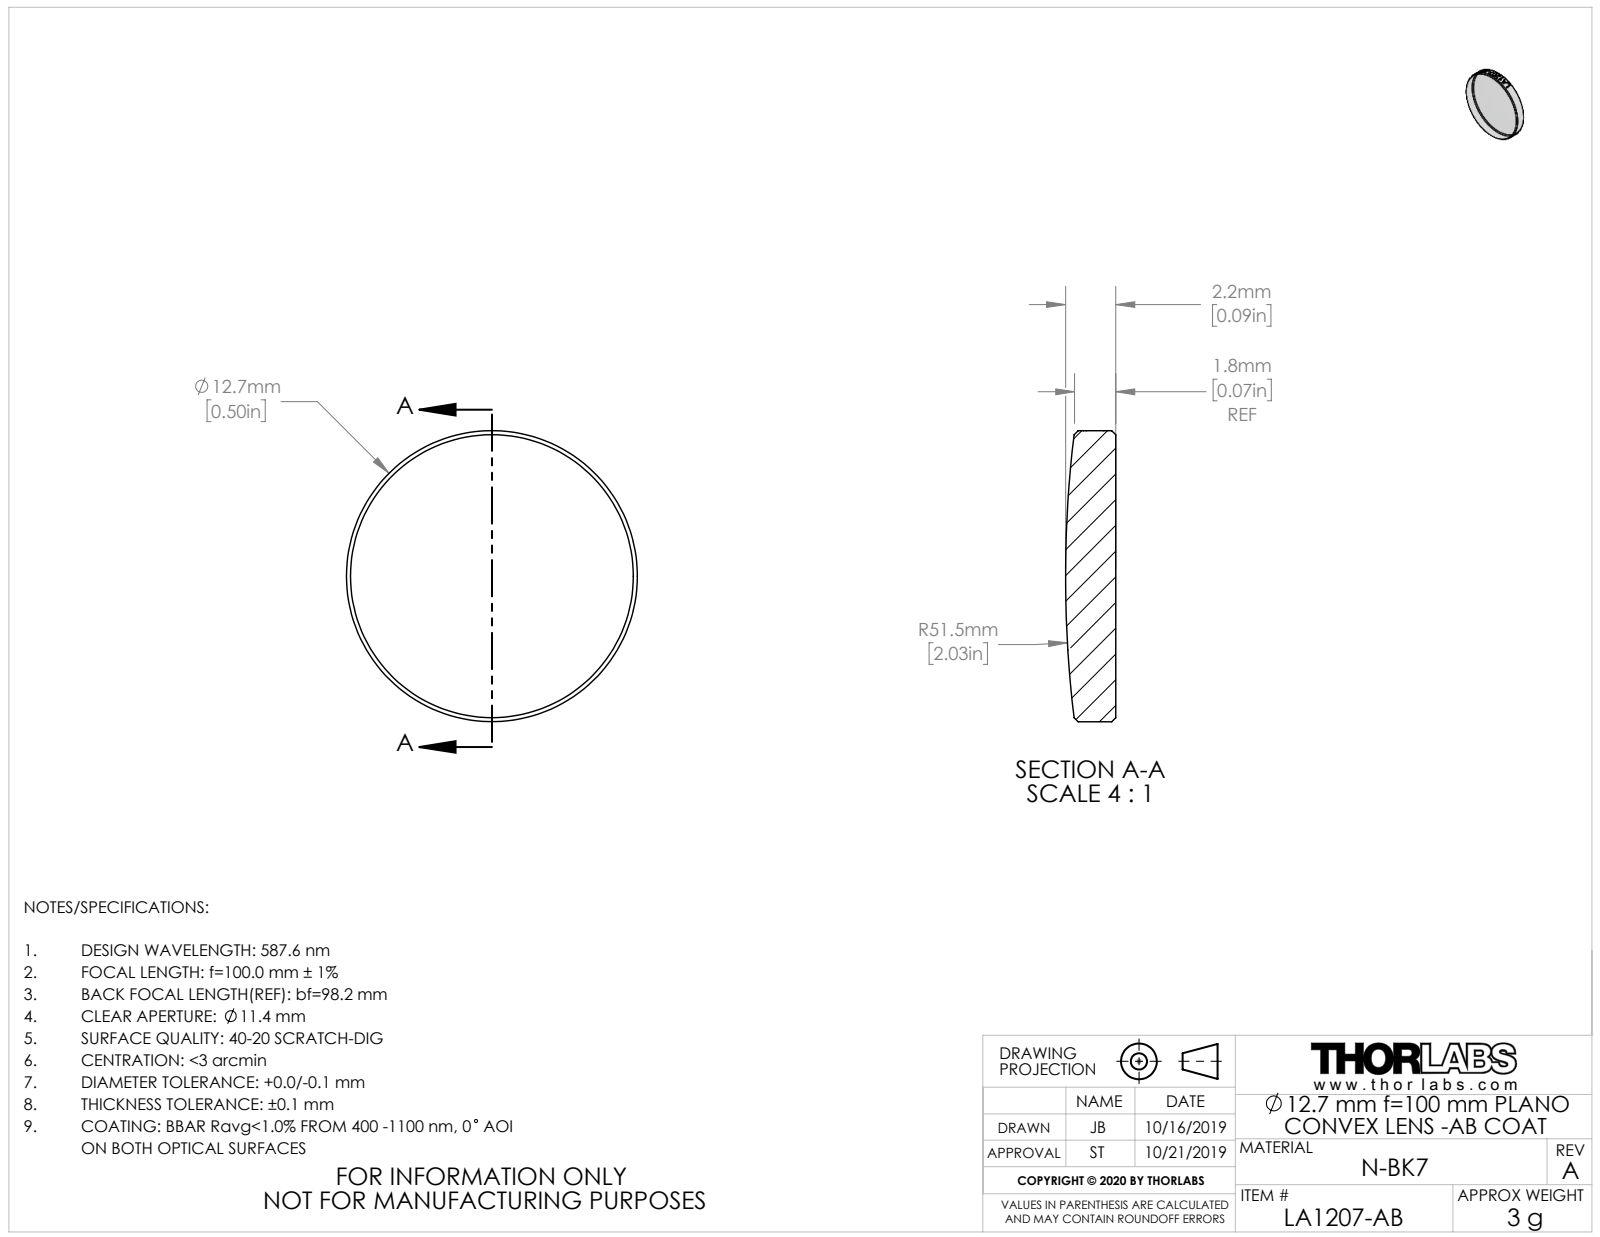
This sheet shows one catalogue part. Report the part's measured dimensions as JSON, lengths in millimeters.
{"part_name": "TTN195794-E0W", "step_written_by": "SolidWorks 2018 (CONFIG_CONTROL_DESIGN)", "units": "millimeters", "bodies": {"solids": 1, "faces": 27, "planar": 1, "cylindrical": 20, "other": 6}, "overall_size": [12.7, 12.7, 2.19], "volume_mm3": 251, "surface_area_mm2": 318, "round_bosses_or_shafts": [[12.7, 1]]}
